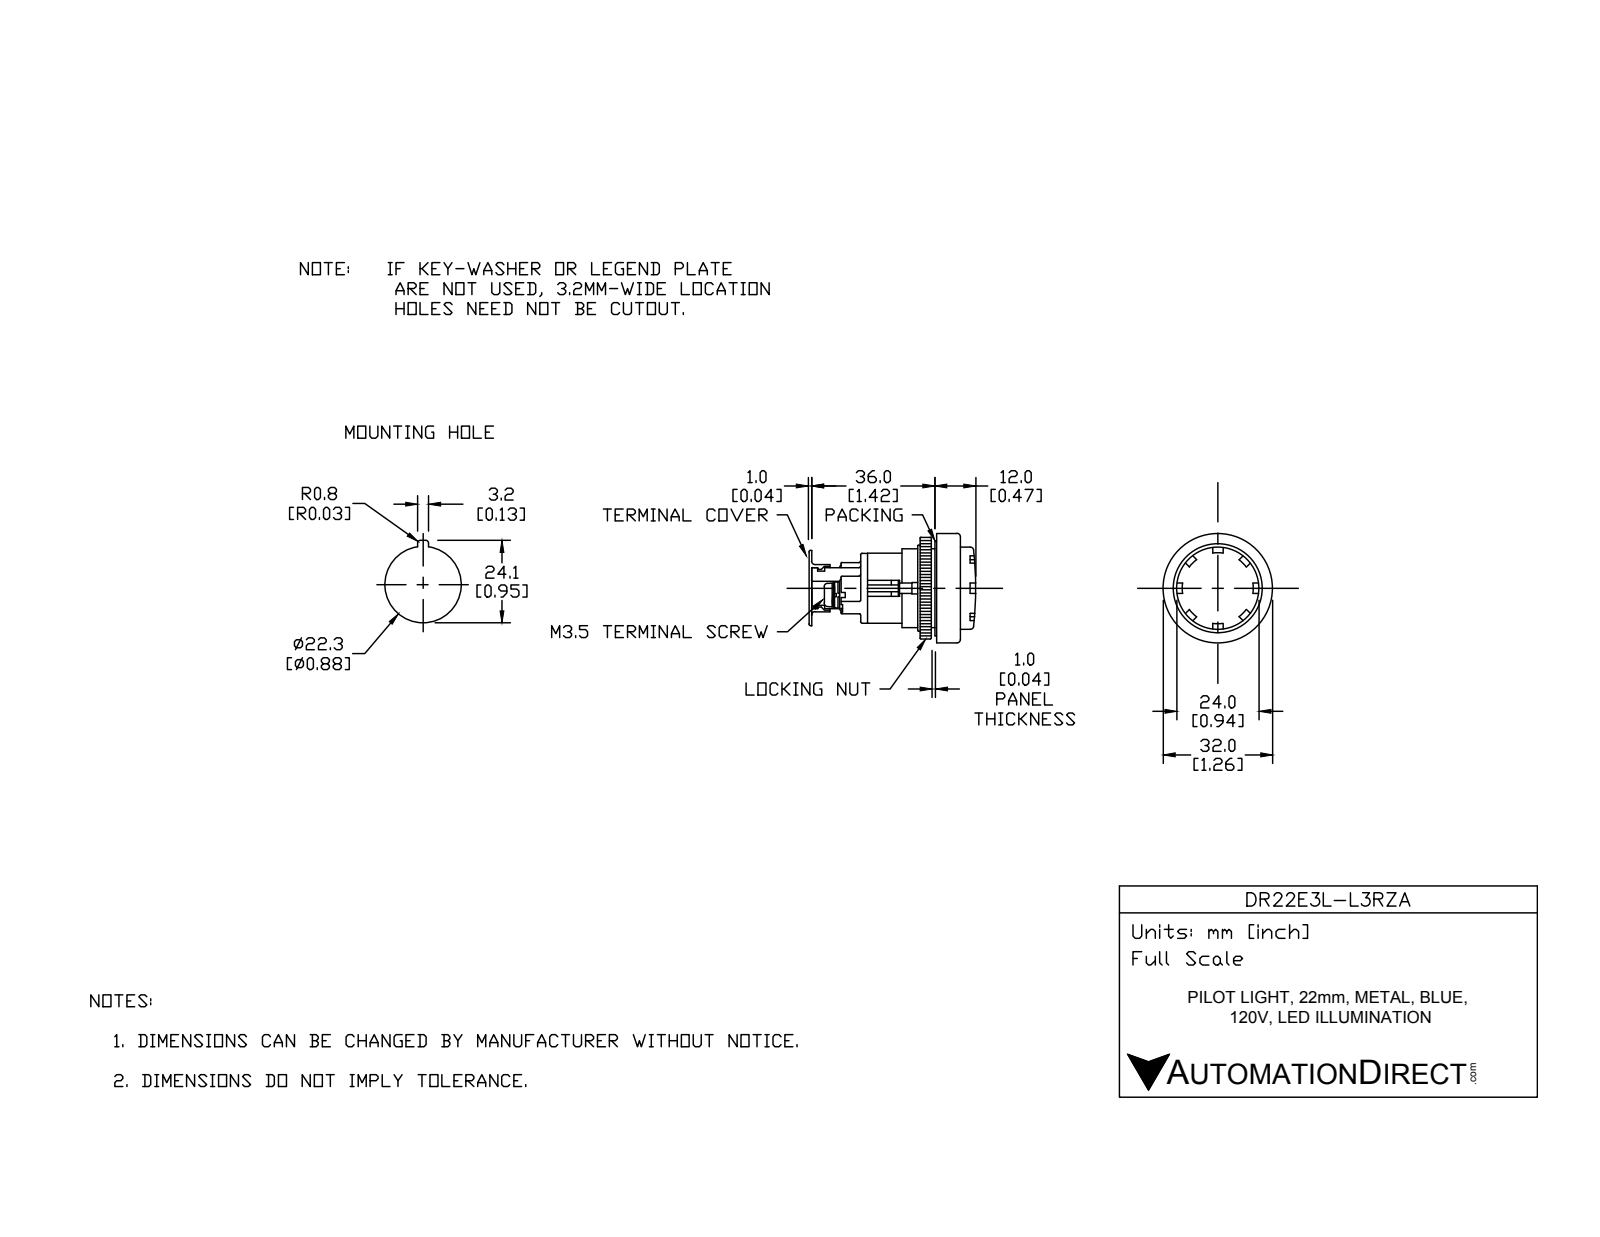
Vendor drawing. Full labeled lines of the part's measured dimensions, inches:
Part name (STEP PRODUCT): DR22E3L-L3SZA
STEP written by: SolidWorks 2017 (AUTOMOTIVE_DESIGN)
Units: inches
Bodies: 12 solids, 232 faces (165 planar, 51 cylindrical, 16 other)
Overall size (bounding box): 2.913 × 1.26 × 1.26
Volume: 2.435 in³ · Surface area: 28.15 in²
Round holes (diameter × count): ⌀0.866 ×1, ⌀0.886 ×1, ⌀0.984 ×1, ⌀1.181 ×1
Round bosses / shafts (diameter × count): ⌀0.217 ×2, ⌀1.26 ×1, ⌀1.169 ×1, ⌀1.161 ×1, ⌀1.063 ×1, ⌀0.858 ×1
Partial cylindrical surfaces — rounded edges, fillets, slot ends (radius × count): R0.02 ×14, R0.128 ×4, R0.039 ×1, R0.197 ×1
Main face-to-face distances: 0.748, 1.181, 1.055, 0.039, 0.157, 0.236, 0.819, 0.433, 1.28, 0.063
